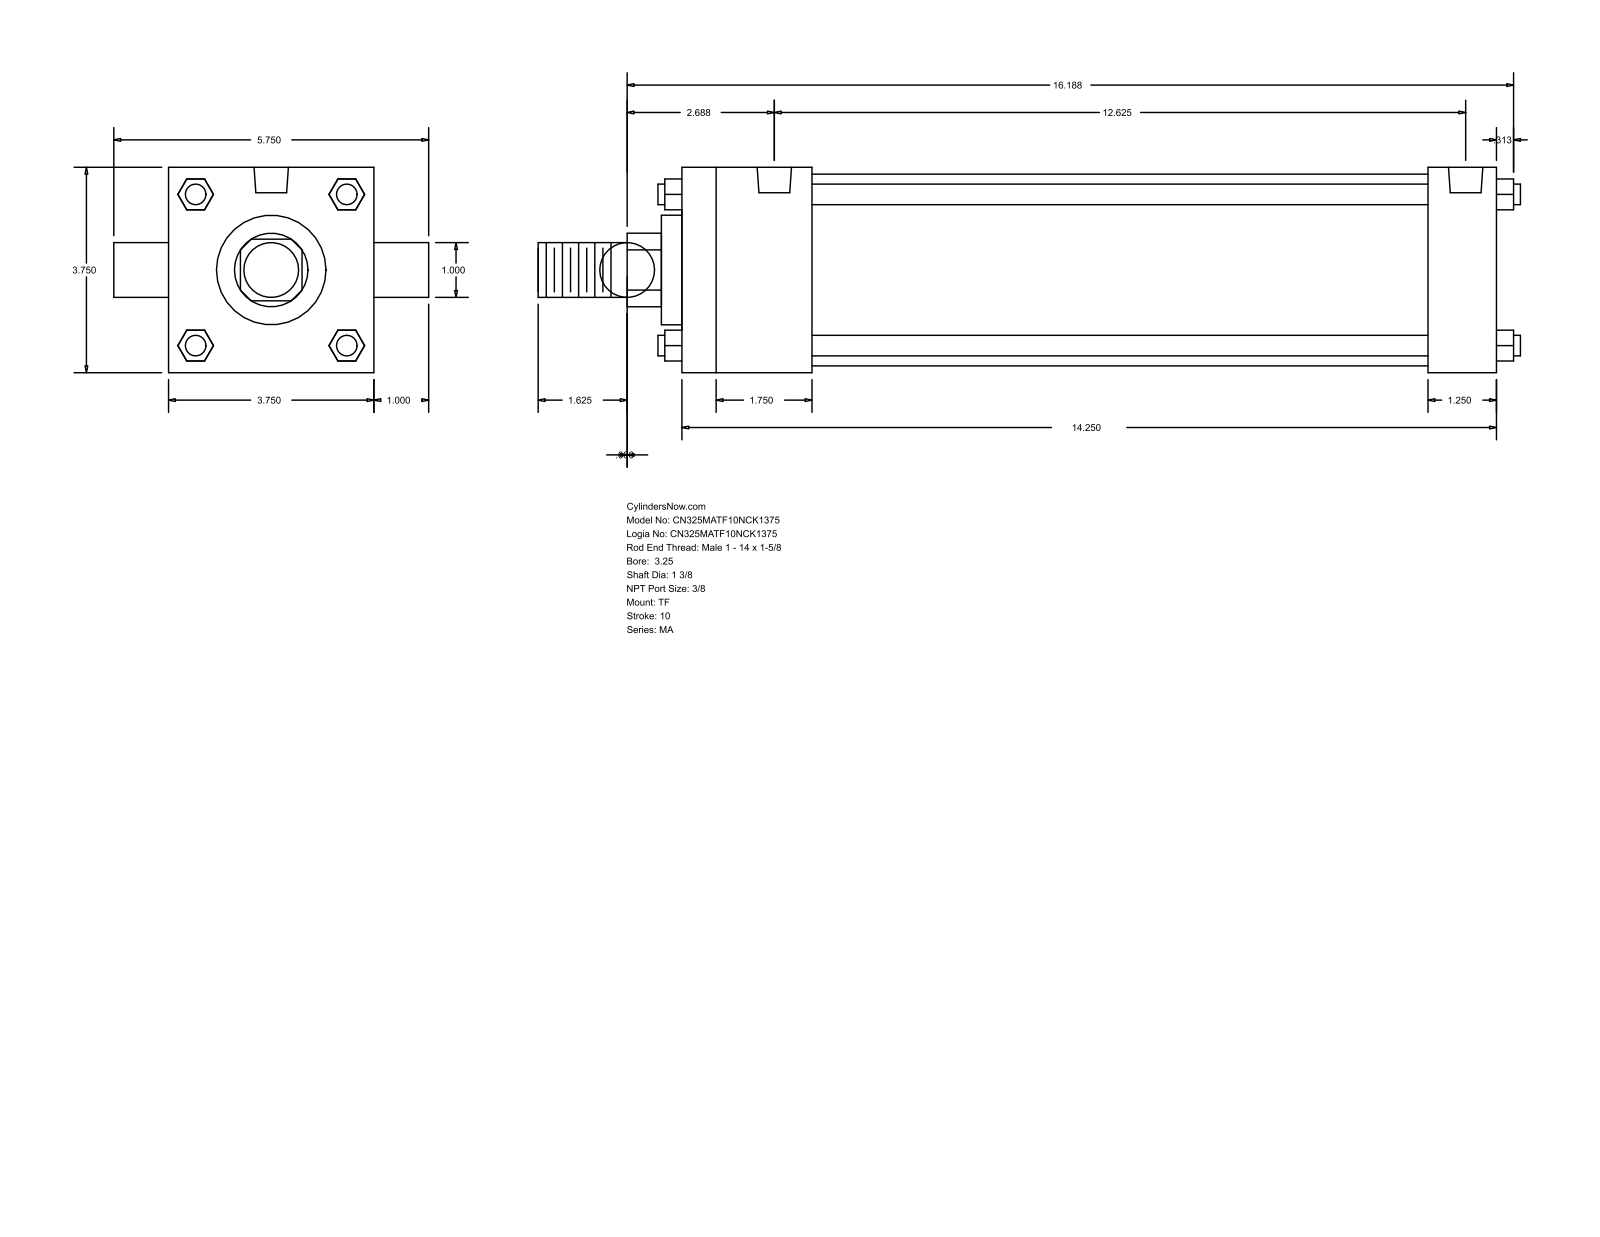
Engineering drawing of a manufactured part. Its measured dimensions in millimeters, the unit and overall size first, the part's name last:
Units: millimetres
Overall size (bounding box): 455.61 × 146.05 × 95.25
Round holes (diameter × count): ⌀11.11 ×3, ⌀15.93 ×2
Round bosses / shafts (diameter × count): ⌀9.53 ×4, ⌀25.4 ×2, ⌀88.9 ×1, ⌀50.8 ×1, ⌀34.92 ×1
Partial cylindrical surfaces — rounded edges, fillets, slot ends (radius × count): R17.06 ×1
Main face-to-face distances: 95.24, 377.83, 60.32, 346.08, 285.76, 317.51, 31.75, 9.52, 69.84, 355.6
Hole centre spacings: 4.76, 4.77, 311.15, 315.91, 315.92, 320.68
Bodies: 0 solids, 120 faces (92 planar, 28 cylindrical, 0 other)
Part name (STEP PRODUCT): MA_TF__0325_1.375
STEP written by: GSSL Pune (CONFIG_CONTROL_DESIGN)
